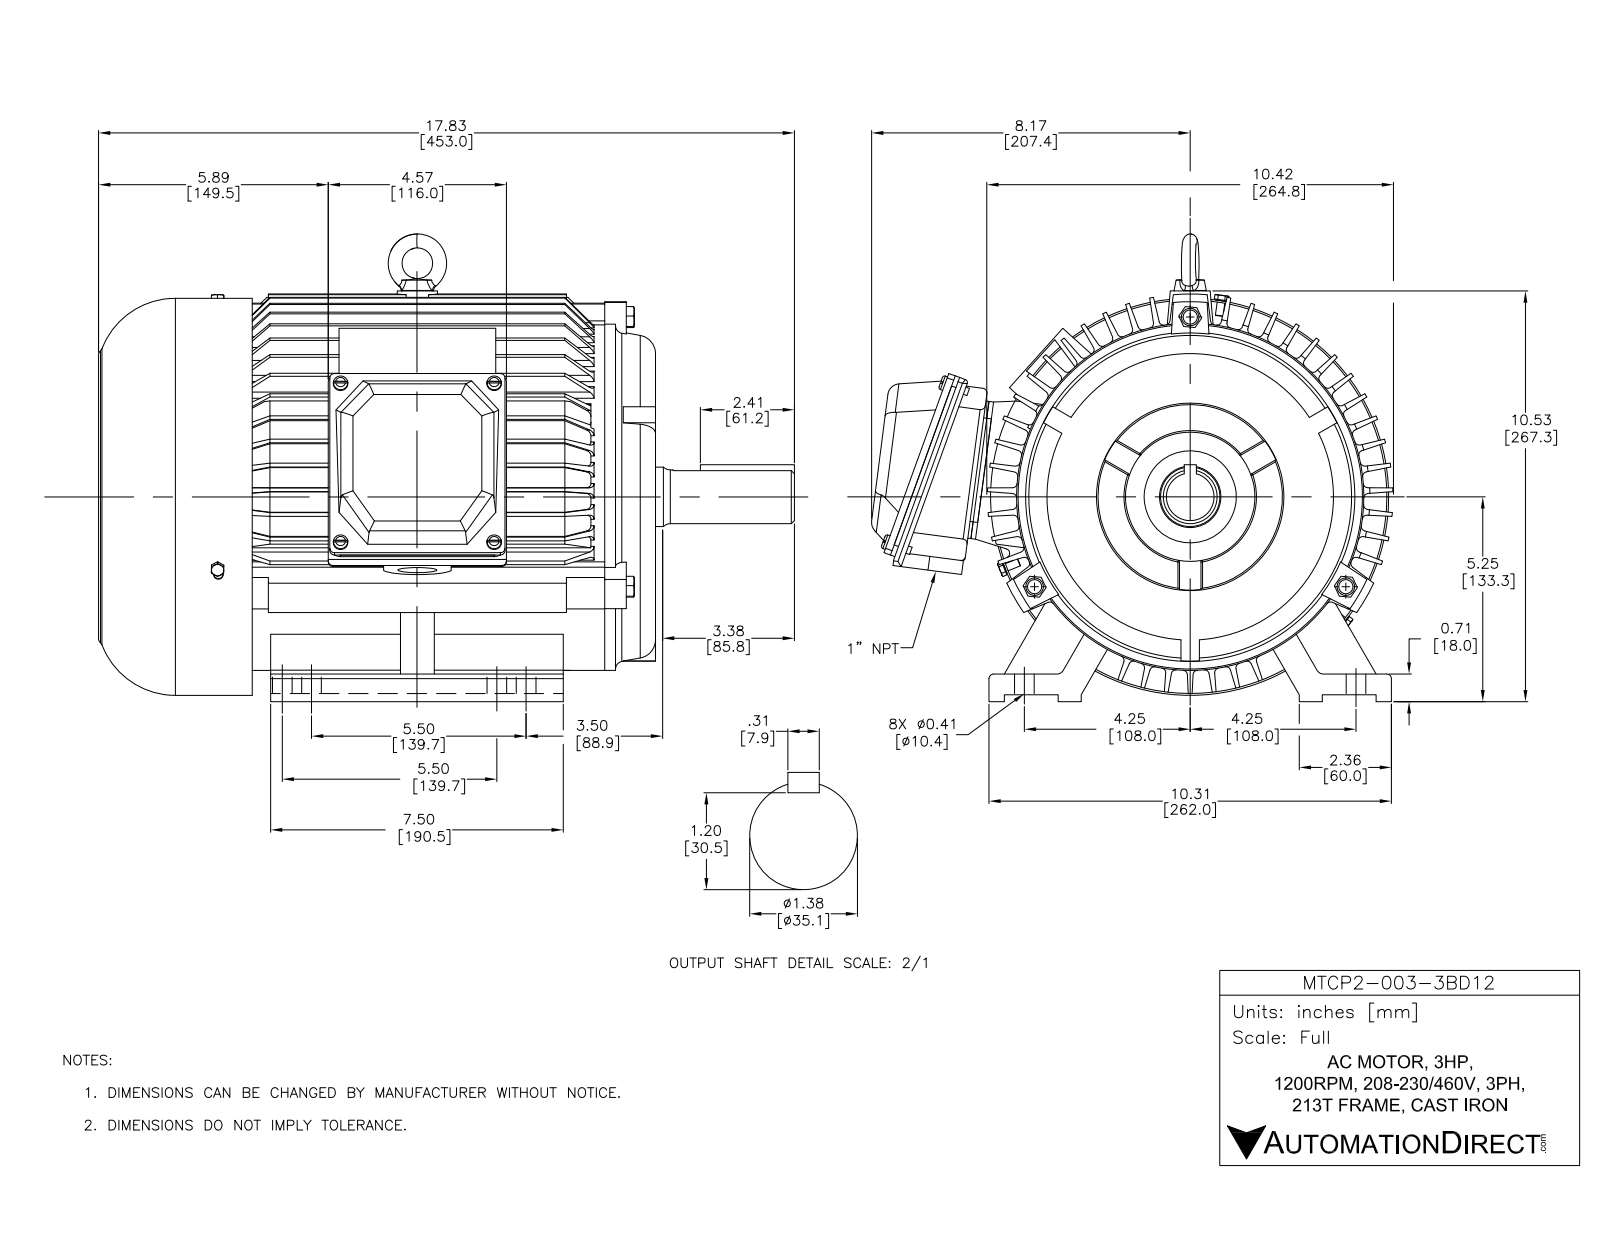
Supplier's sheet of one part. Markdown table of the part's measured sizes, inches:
| quantity | value |
| --- | --- |
| part name | PEWWE-213T |
| STEP written by | SolidWorks 2017 (AUTOMOTIVE_DESIGN) |
| units | inches |
| bodies | 18 solids, 1759 faces (1036 planar, 462 cylindrical, 261 other) |
| overall size | 17.835 × 13.363 × 11.986 |
| volume | 238 in³ |
| surface area | 1 894 in² |
| round holes (diameter × count) | 0.228 × 8, 0.197 × 6, 0.165 × 4, 0.236 × 4, 0.276 × 4, 0.433 × 4, 0.315 × 3, 0.362 × 3, 0.394 × 3, 0.335 × 1, 0.453 × 1, 1 × 1 |
| round bosses / shafts (diameter × count) | 0.197 × 7, 0.283 × 3, 10.173 × 1, 10.079 × 1, 8.898 × 1, 5.118 × 1, 4.173 × 1, 3.317 × 1 |
| partial cylindrical surfaces (radius × count) | 0.118 × 104, 0.276 × 17, 0.039 × 12, 0.059 × 8, 0.157 × 8, 0.315 × 8, 0.091 × 6, 0.433 × 6 |
| main face-to-face distances | 0.709, 0.157, 14.167, 0.047, 14.215, 0.177, 0.531, 0.039, 0.236, 13.978 |
| hole center spacings | 3.937, 2.677, 4.331, 5.853, 2.678, 3.786, 4.331, 5.853 |
